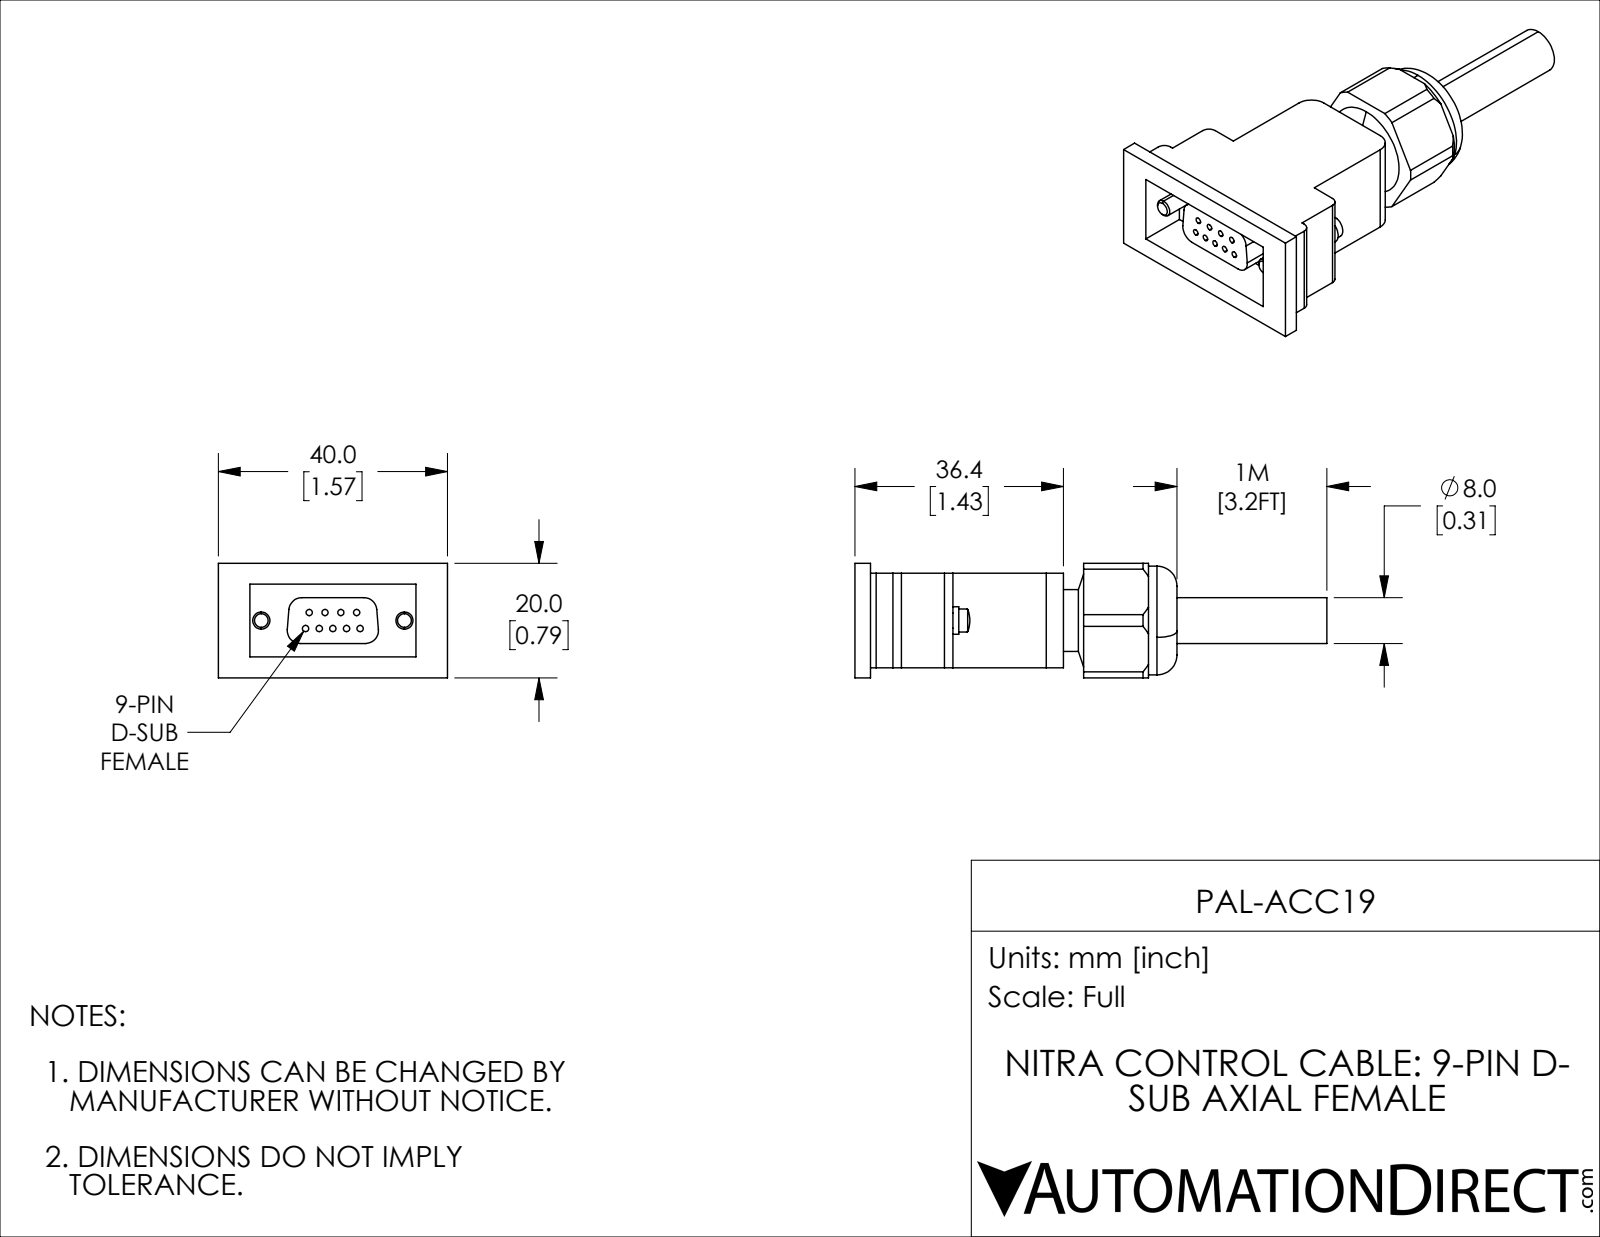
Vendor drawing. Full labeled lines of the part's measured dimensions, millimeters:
Part name (STEP PRODUCT): PAL-ACC19
STEP written by: SolidWorks 2019 (CONFIG_CONTROL_DESIGN)
Units: millimetres
Bodies: 1 solid, 139 faces (61 planar, 56 cylindrical, 22 other)
Overall size (bounding box): 82.4 × 40 × 20
Volume: 20 838 mm³ · Surface area: 8 406 mm²
Round holes (diameter × count): ⌀1.1 ×9, ⌀10.6 ×1
Round bosses / shafts (diameter × count): ⌀4.8 ×2, ⌀4 ×2, ⌀3 ×2, ⌀19 ×1, ⌀10.8 ×1, ⌀8 ×1
Partial cylindrical surfaces — rounded edges, fillets, slot ends (radius × count): R1.5 ×4, R2.25 ×4, R1 ×2, R3 ×2, R11 ×1
Main face-to-face distances: 16.5, 20, 1.9, 14.6, 1.75, 3.65, 16.35, 18.25, 6, 26
Hole centre spacings: 2.76, 2.38, 4.76, 2.87, 4.38, 4.96, 5.52, 7.14
